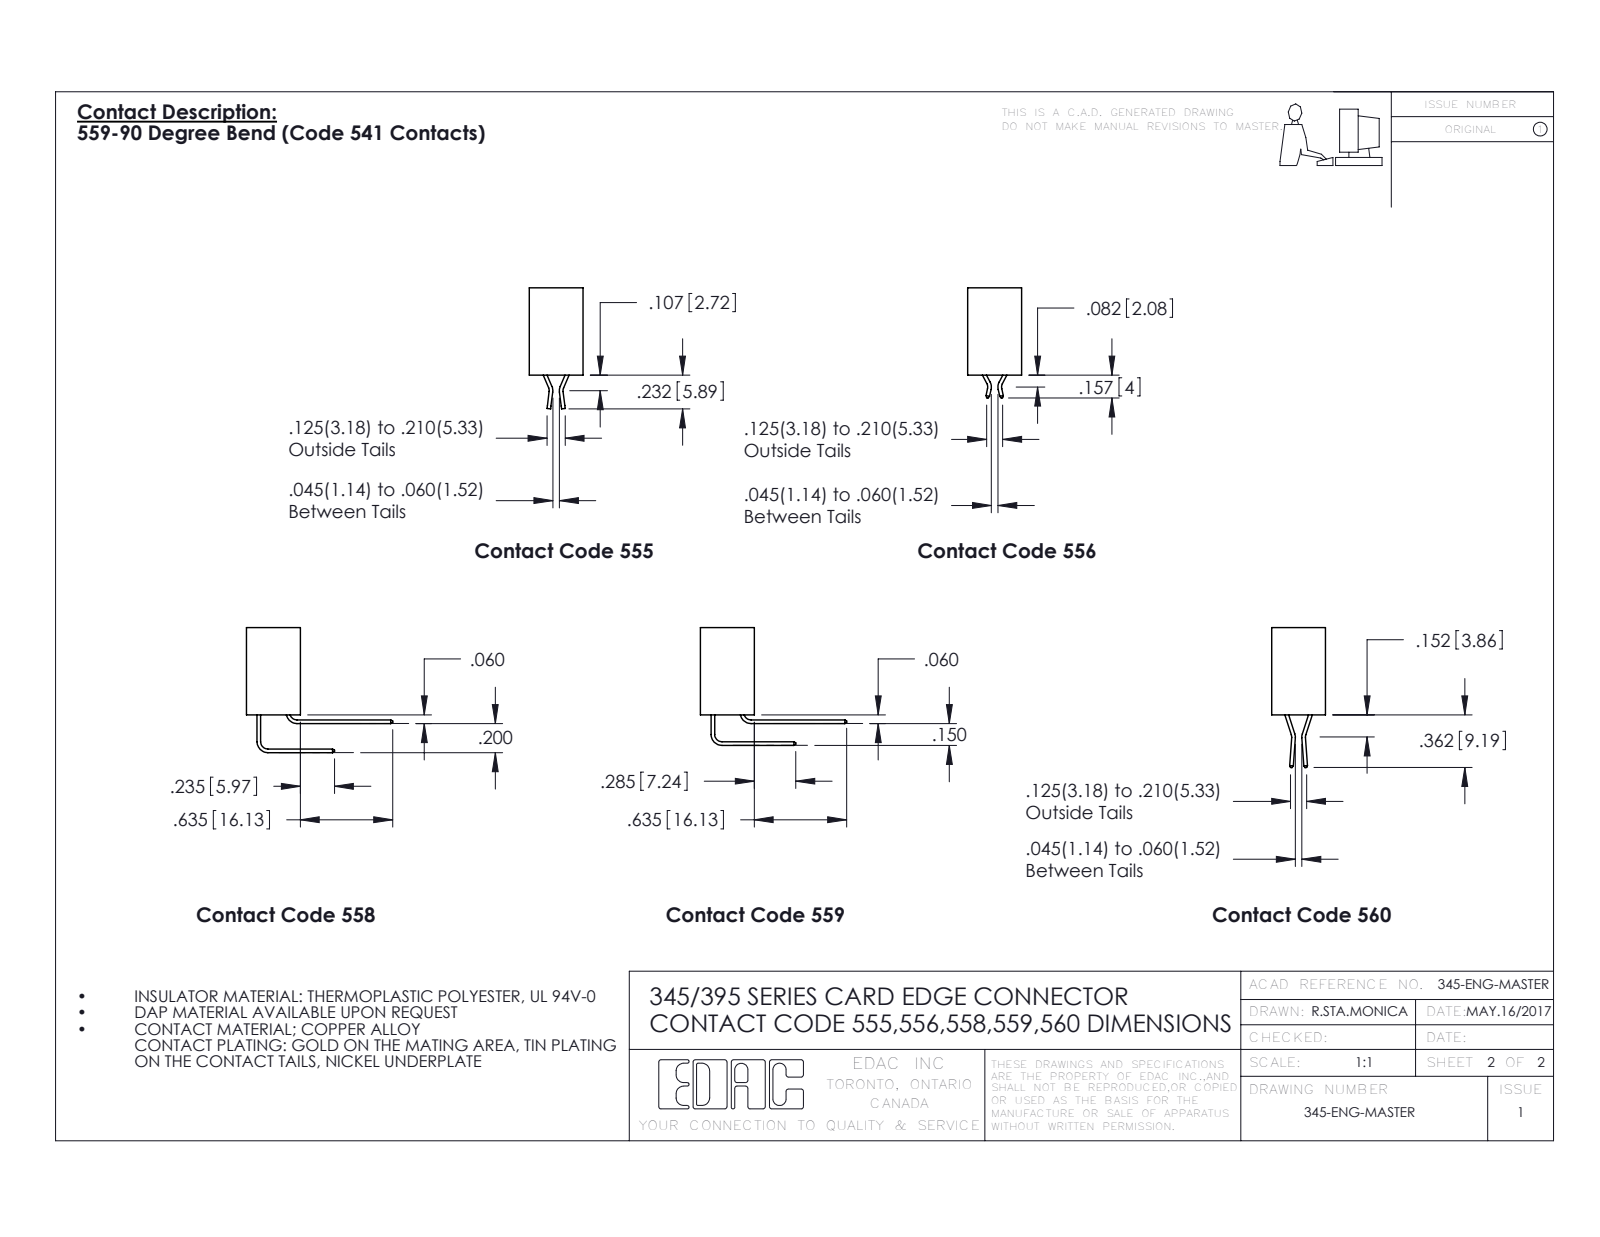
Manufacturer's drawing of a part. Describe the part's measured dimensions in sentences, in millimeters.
The part is named "345-292-001_345-293-144; 345 Part_No Mounting Lugs; 395-008-544-101". Its 3-D file was written by "SolidWorks 2016 (CONFIG_CONTROL_DESIGN)". It is 9 solids with 534 faces: 364 planar, 170 cylindrical and 0 other. Overall it measures 34 by 26.9 by 9.4 millimeters. Its volume is 2 950 cubic millimeters and its surface area 3 934 square millimeters. Round holes: 1 of diameter 1.6. Partial cylindrical surfaces (rounded edges, fillets, slot ends): 22 of radius 0.3, 16 of radius 0.2, 6 of radius 0.2, 6 of radius 0.8, 3 of radius 0.7, 2 of radius 0.8, 2 of radius 1, 1 of radius 0.4. The main face-to-face distances are 5.1, 1.8, 7.6, 2.5, 2.5, 6.9, 0.6, 9.4, 7.6, 1.5.
